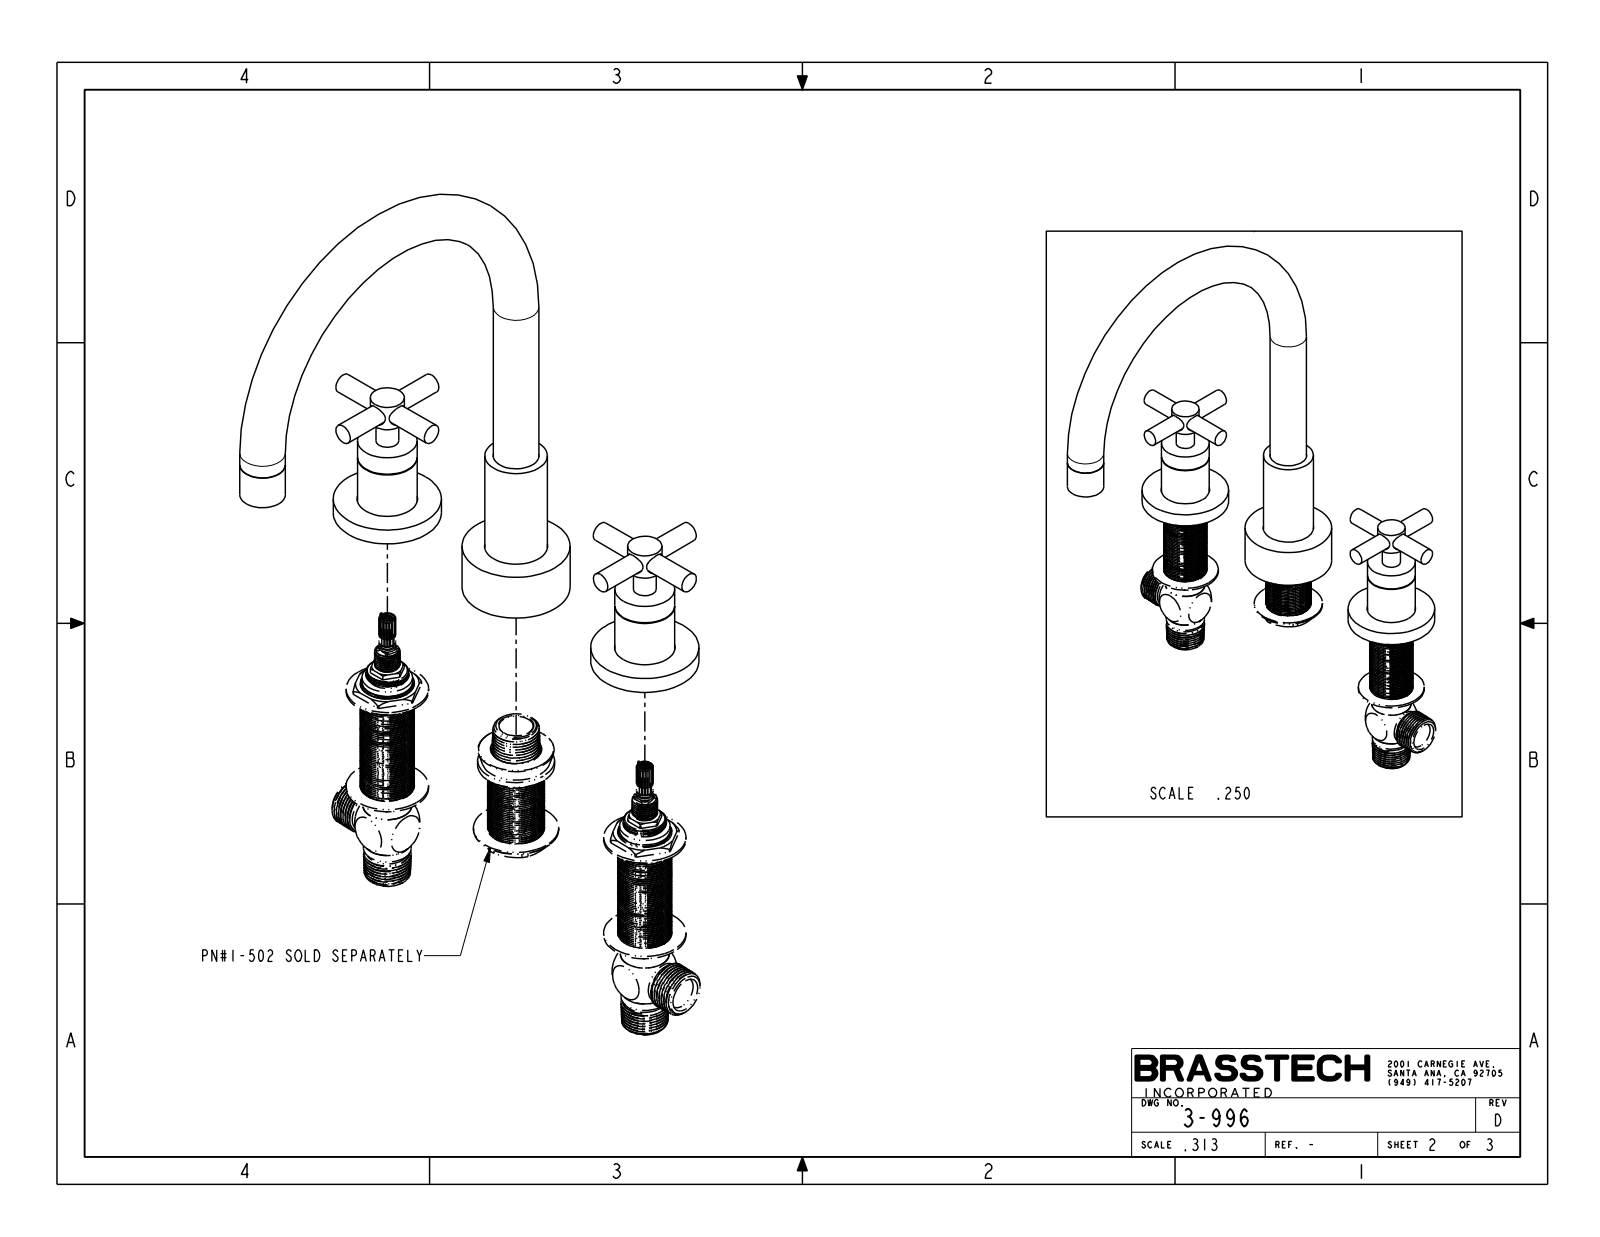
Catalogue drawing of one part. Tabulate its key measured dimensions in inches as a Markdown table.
| quantity | value |
| --- | --- |
| part name | 3-996 |
| STEP written by | CREO PARAMETRIC BY PTC INC, 2018400 (CONFIG_CONTROL_DESIGN) |
| units | inches |
| bodies | 3 solids, 100 faces (34 planar, 64 cylindrical, 2 other) |
| overall size | 11.978 × 10.75 × 9.75 |
| volume | 31.76 in³ |
| surface area | 142.1 in² |
| round holes (diameter × count) | 0.47 × 3 |
| round bosses / shafts (diameter × count) | 2.375 × 3, 0.445 × 3, 1.313 × 2, 1 × 2, 0.75 × 2, 0.5 × 2, 0.4 × 2, 1.375 × 1 |
| main face-to-face distances | 0.375, 1.103, 0.728, 1.483, 1.503, 1.108, 1.128, 0.38, 0.4, 0.02 |
| hole center spacings | 8 |
